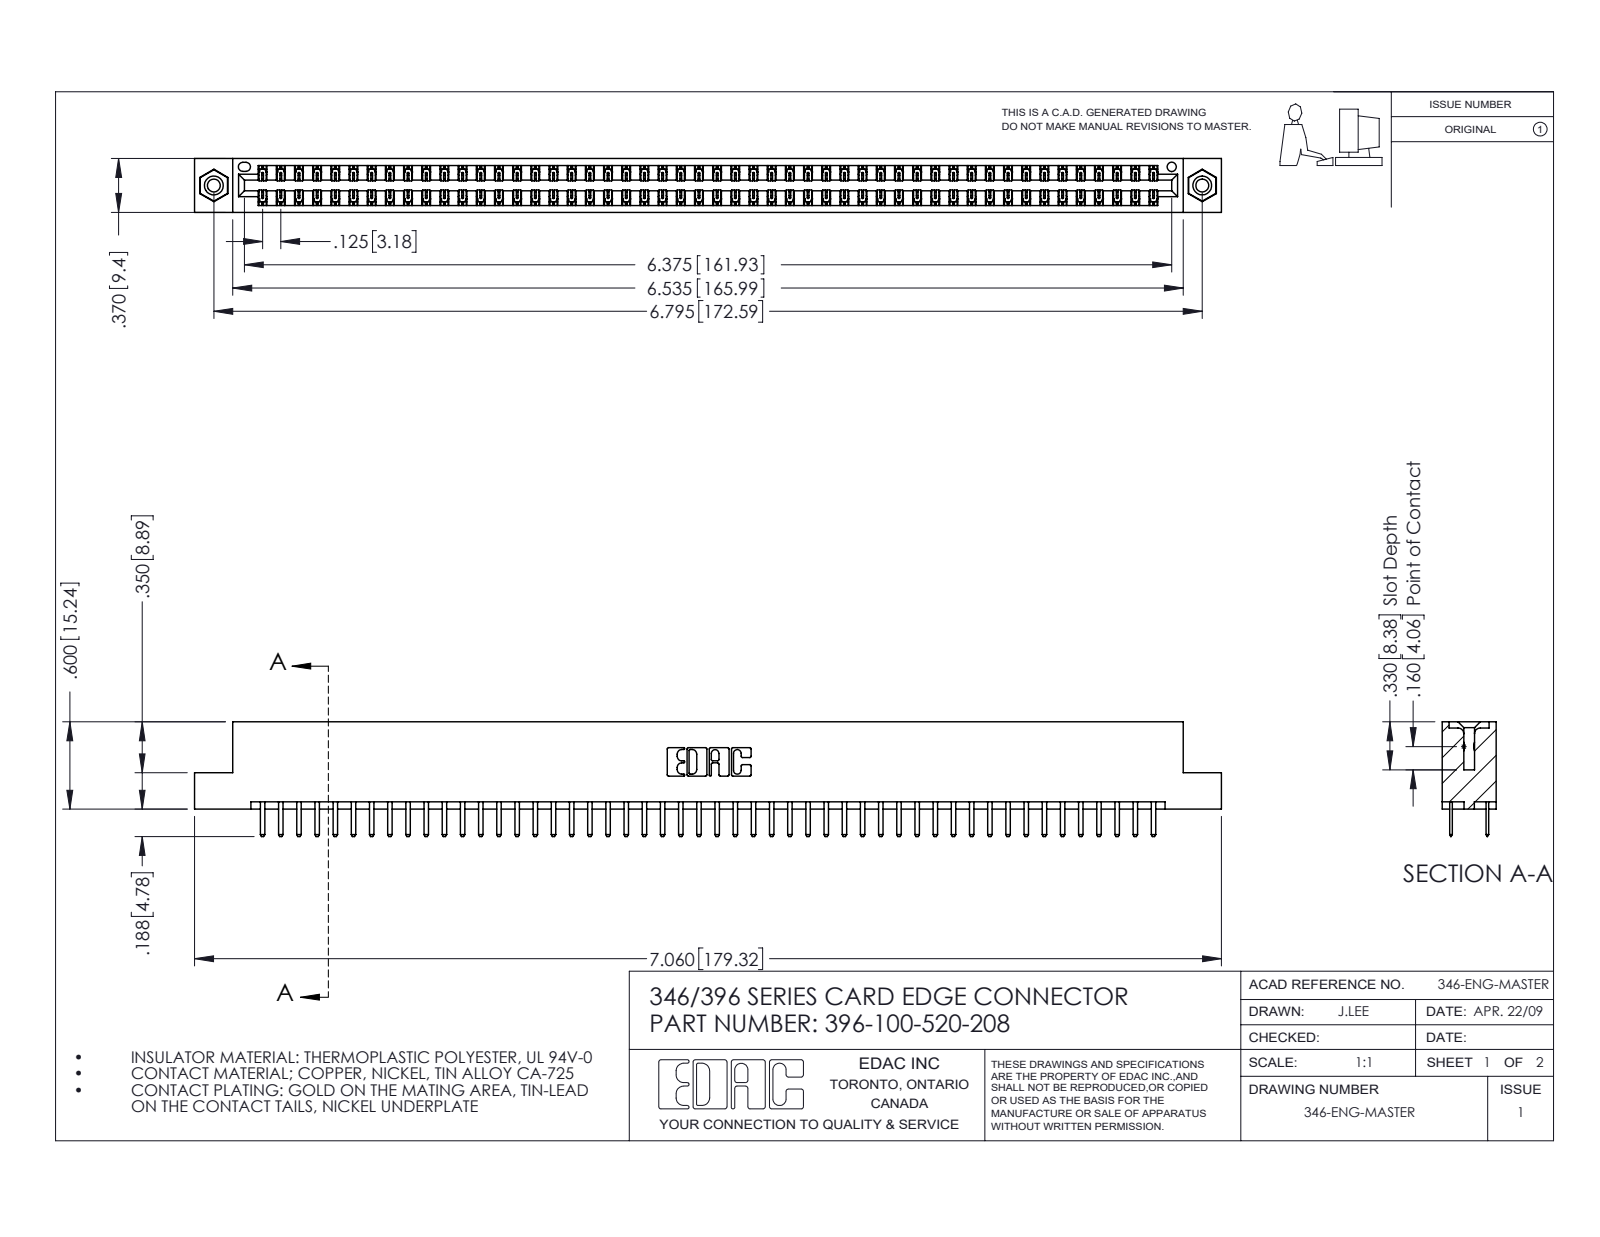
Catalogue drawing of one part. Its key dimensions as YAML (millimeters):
part_name: "346 Part_Flush Mounting Lugs - 0.156 Dia-TI; 345-250-001_345-250-003-102; 396-100-520-208; 345-292-001_345-293-120"
step_written_by: "SolidWorks 2016 (CONFIG_CONTROL_DESIGN)"
units: millimeters
bodies: {solids: 103, faces: 5782, planar: 3808, cylindrical: 1958, other: 16}
overall_size: [179.3, 20, 9.4]
volume: 17500
surface_area: 24100
round_holes:
  - {diameter: 2.3, count: 2}
  - {diameter: 3.2, count: 2}
  - {diameter: 4, count: 2}
  - {diameter: 1.6, count: 1}
round_bosses_or_shafts:
  - {diameter: 3.9, count: 2}
partial_cylinders:
  - {radius: 0.2, count: 150}
  - {radius: 0.3, count: 104}
  - {radius: 0.3, count: 22}
  - {radius: 0.2, count: 6}
  - {radius: 0.8, count: 6}
  - {radius: 0.7, count: 3}
  - {radius: 0.4, count: 2}
  - {radius: 0.6, count: 2}
face_to_face_distances: [1.2, 8.2, 6.4, 9.4, 7, 1.8, 7.6, 0.6, 3.8, 5.6]
hole_center_spacings: [6.2, 167.3, 172.6]
